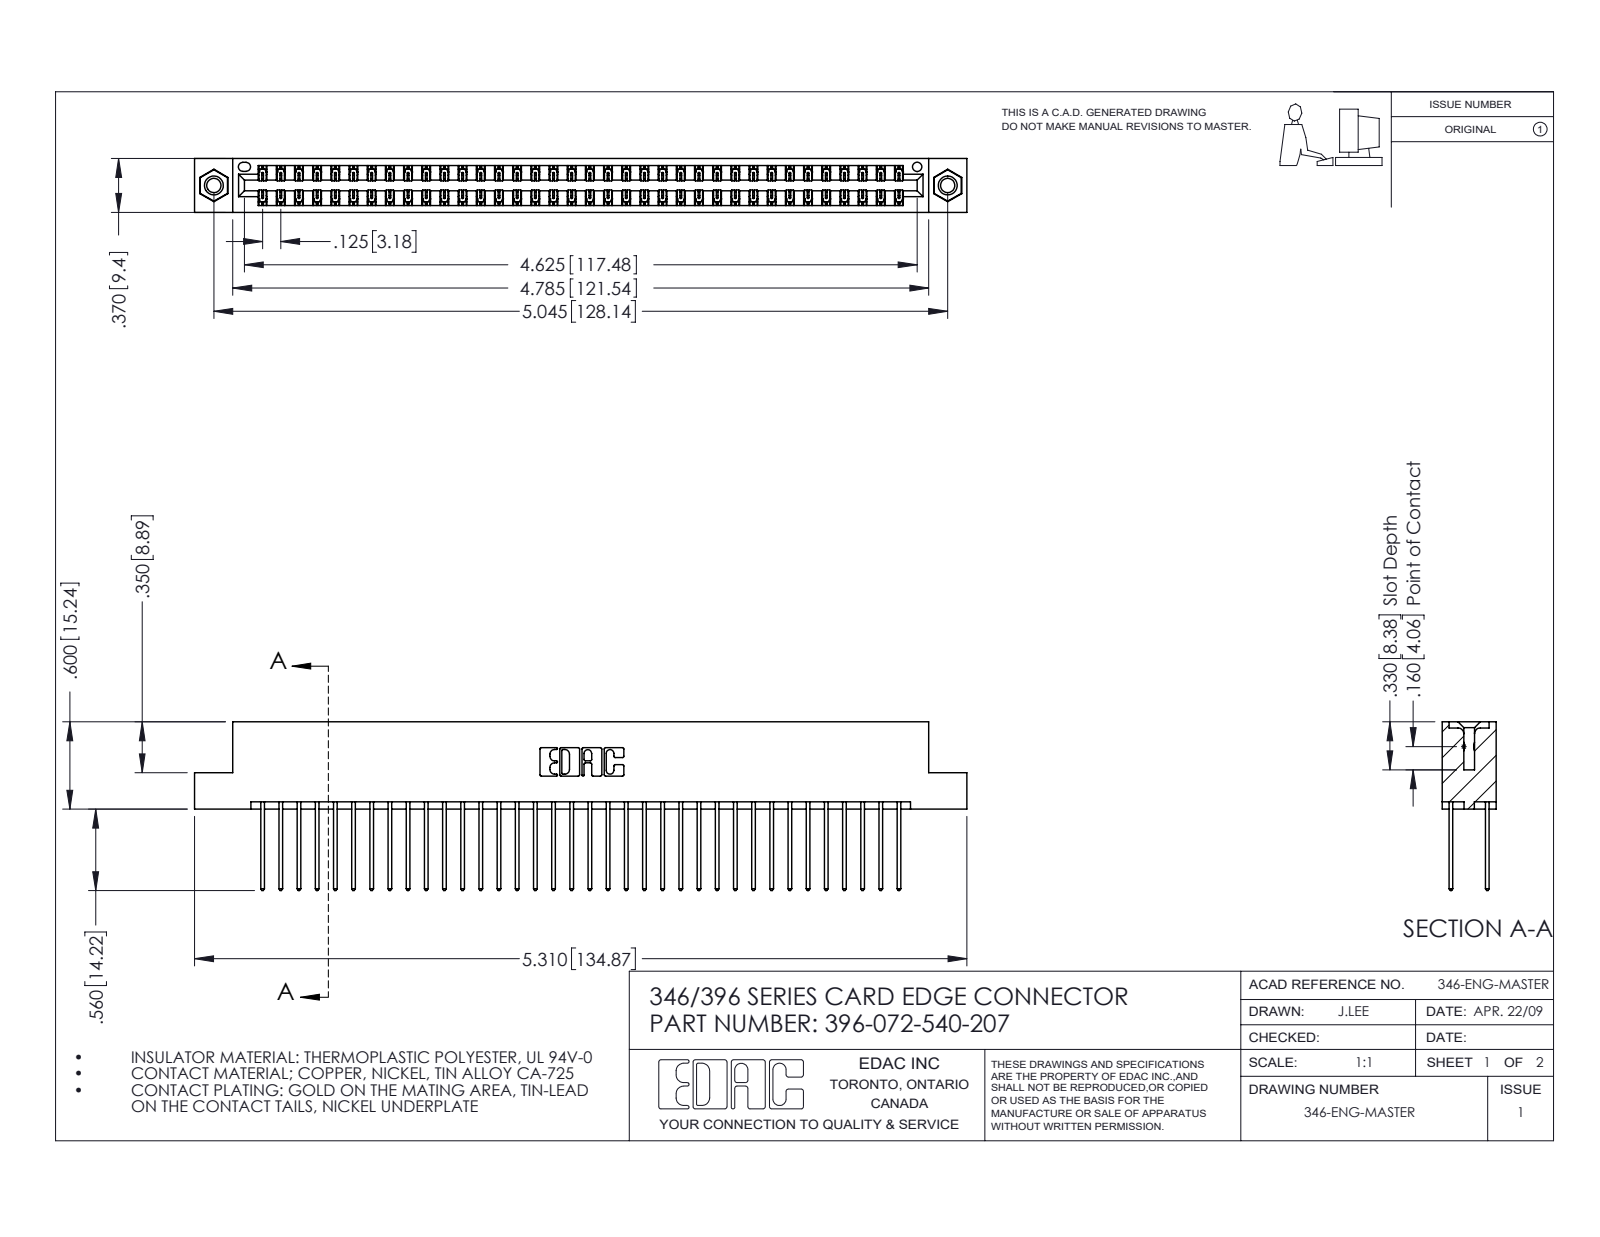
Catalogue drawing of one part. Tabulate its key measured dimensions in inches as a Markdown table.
| quantity | value |
| --- | --- |
| part name | 396-072-540-207; 346 Part_Flush Mounting Lugs - 0.156 Dia-TI; 345-250-001_345-250-005-103; 345-292-001_345-293-140 |
| STEP written by | SolidWorks 2016 (CONFIG_CONTROL_DESIGN) |
| units | inches |
| bodies | 75 solids, 3926 faces (2628 planar, 1282 cylindrical, 16 other) |
| overall size | 5.31 × 1.16 × 0.37 |
| volume | 0.816 in³ |
| surface area | 30.38 in² |
| round holes (diameter × count) | 0.098 × 2, 0.125 × 2, 0.156 × 2, 0.064 × 1 |
| round bosses / shafts (diameter × count) | 0.155 × 2 |
| partial cylindrical surfaces (radius × count) | 0.006 × 108, 0.01 × 72, 0.01 × 22, 0.007 × 6, 0.031 × 6, 0.026 × 3, 0.014 × 2, 0.022 × 2 |
| main face-to-face distances | 0.048, 0.322, 0.25, 0.072, 0.298, 0.025, 0.37, 0.275, 0.148, 0.222 |
| hole center spacings | 0.246, 4.836, 5.045 |
